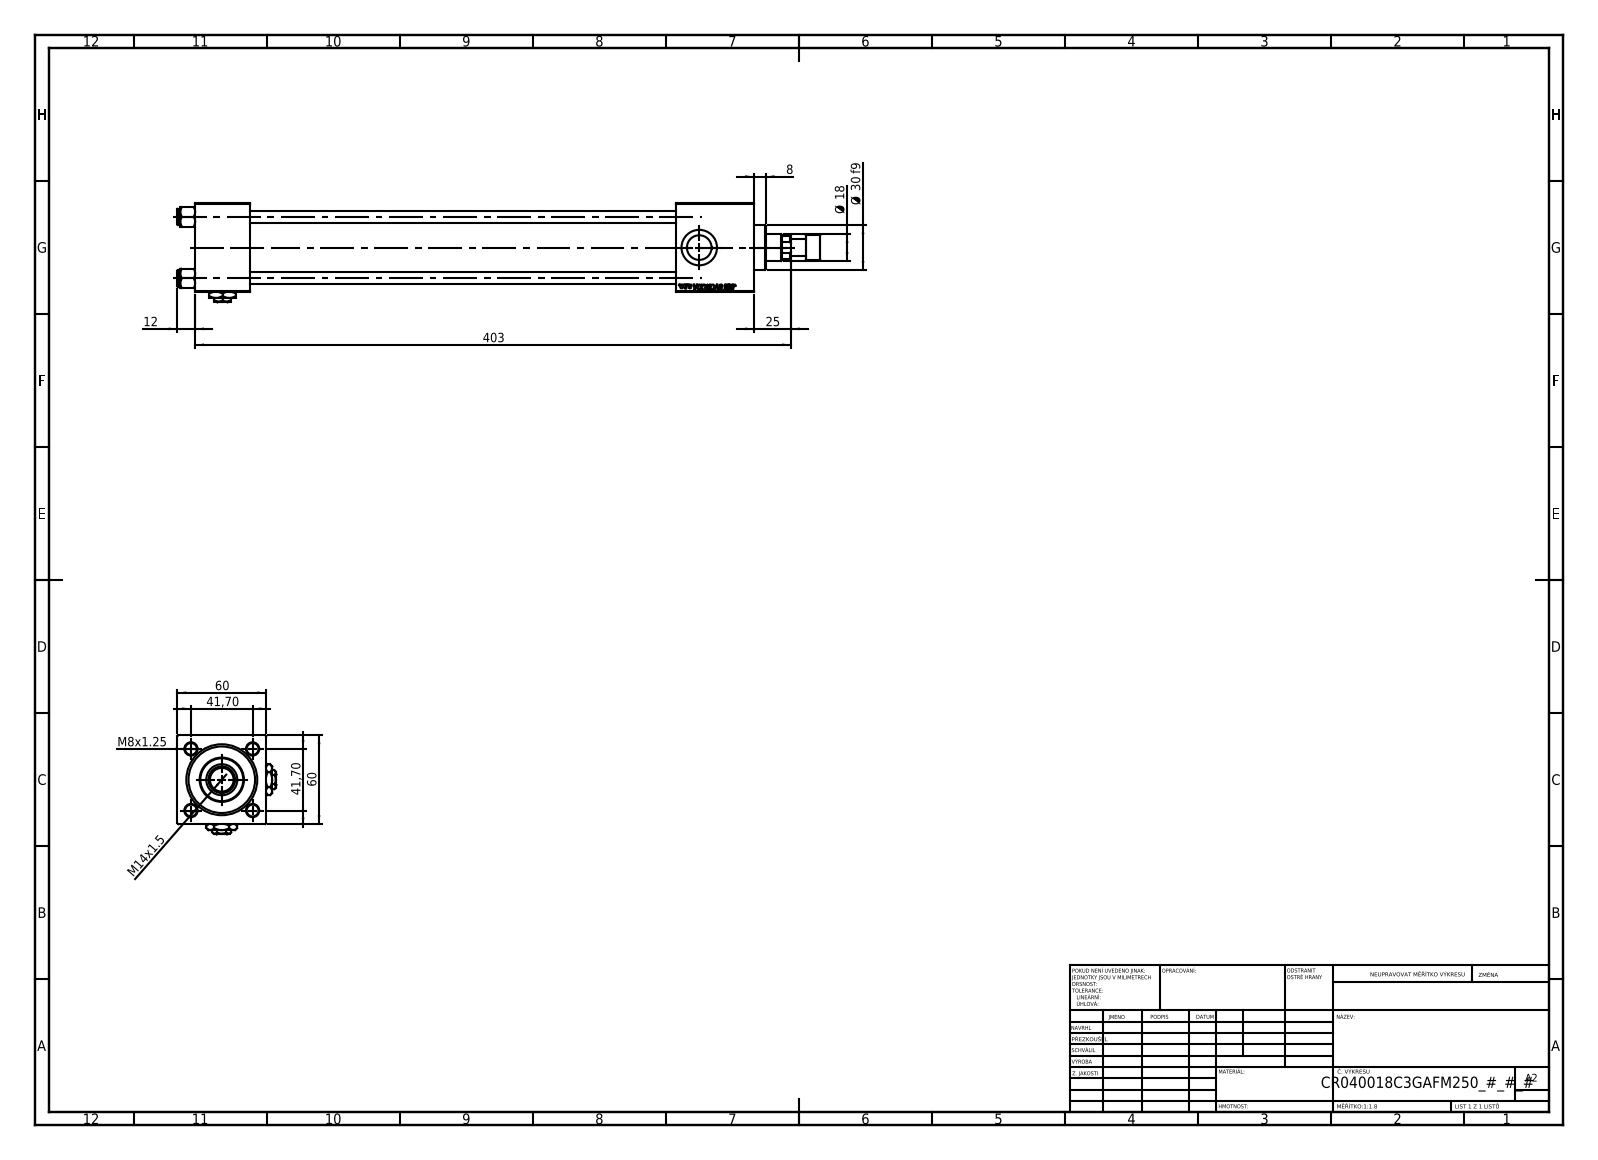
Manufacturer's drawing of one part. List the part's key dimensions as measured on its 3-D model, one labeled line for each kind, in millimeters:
Part name (STEP PRODUCT): V215_VC_A; V215CR_VCP_C; V215CR_ROD_END_F; Zatka_pro_OIL_PORT (+3 more)
STEP written by: SolidWorks 2019 (CONFIG_CONTROL_DESIGN)
Units: millimetres
Bodies: 14 solids, 1261 faces (577 planar, 102 cylindrical, 582 other)
Overall size (bounding box): 435 × 67 × 67
Volume: 600 039 mm³ · Surface area: 207 915 mm²
Round holes (diameter × count): ⌀8 ×4, ⌀7 ×2, ⌀16.66 ×2, ⌀24 ×2, ⌀8.5 ×1, ⌀18 ×1, ⌀21 ×1, ⌀31 ×1, ⌀40 ×1, ⌀45 ×1
Round bosses / shafts (diameter × count): ⌀11 ×5, ⌀46 ×1, ⌀30 ×1, ⌀17 ×1
Main face-to-face distances: 60, 37, 378, 341, 53, 325, 288, 349.3, 312.3, 24.3
Hole centre spacings: 29.49, 41.7, 58.97
